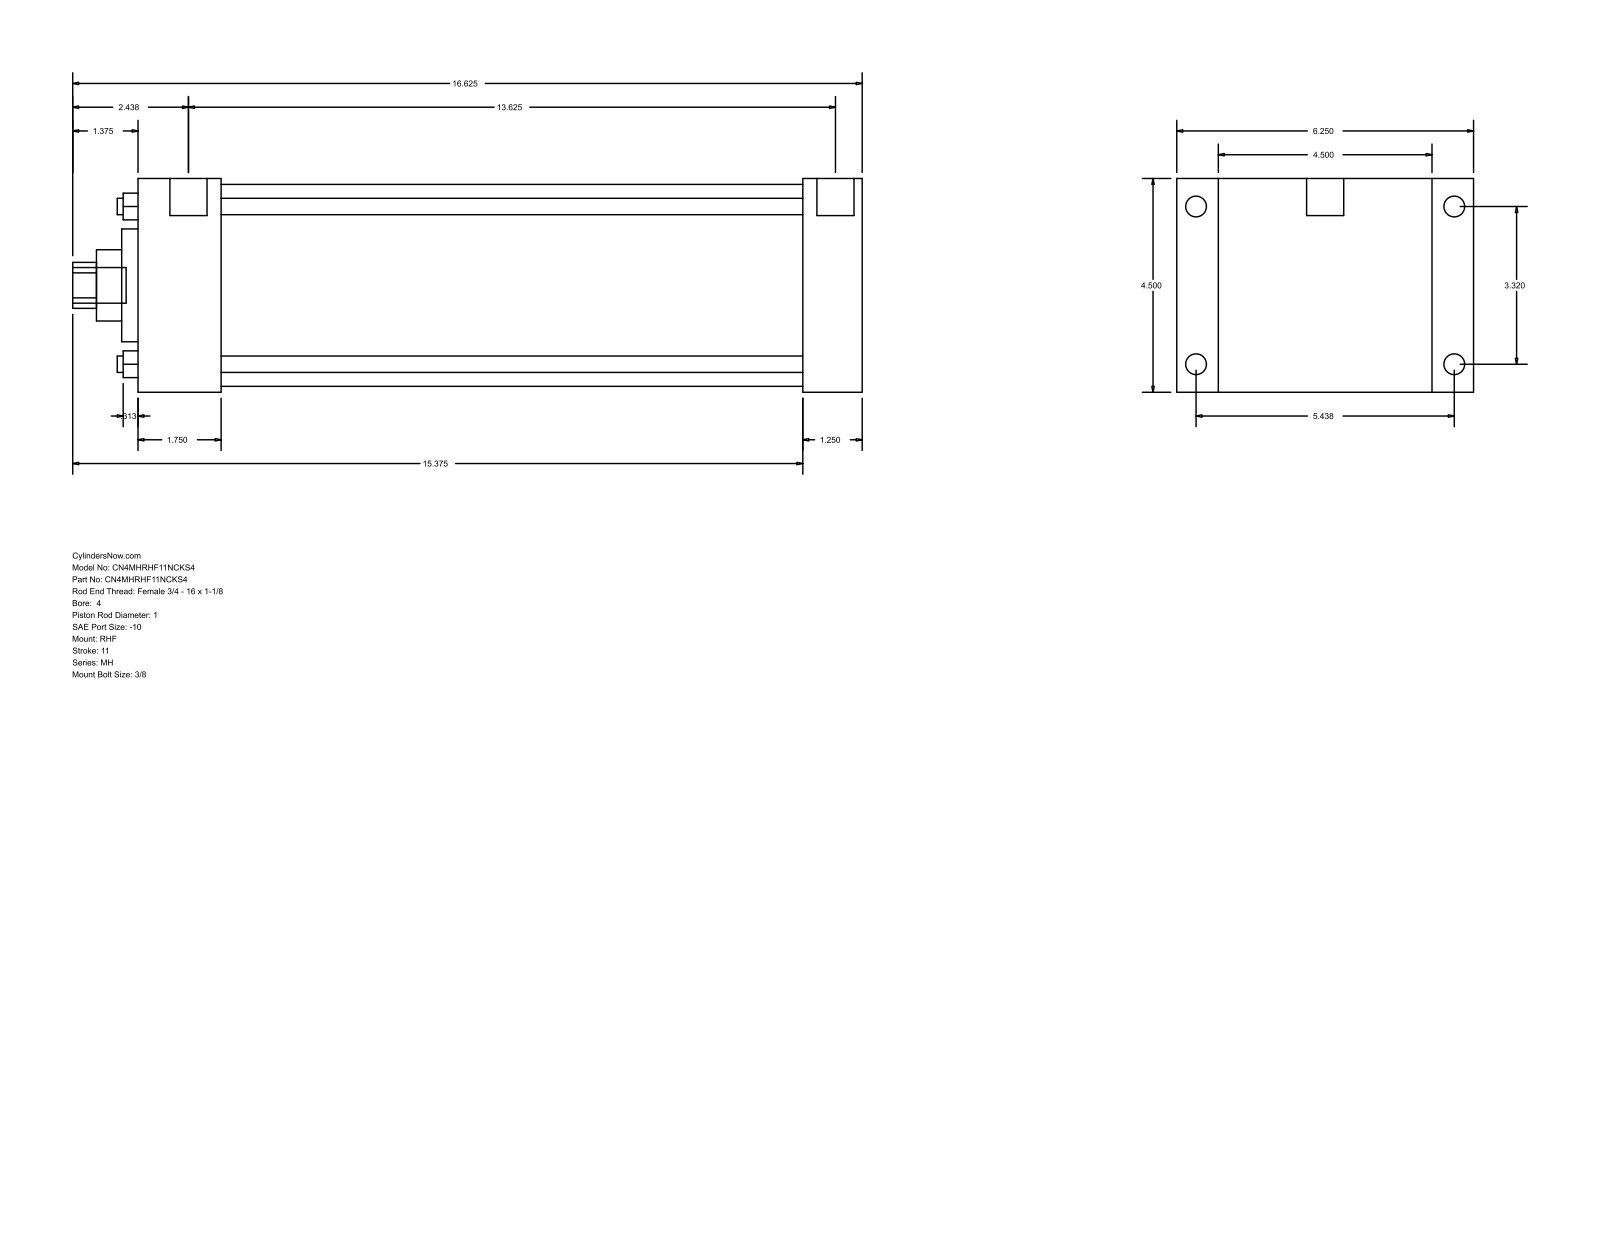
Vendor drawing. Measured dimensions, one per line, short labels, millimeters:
name: MH_RHF__0400_1
written by: GSSL Pune (CONFIG_CONTROL_DESIGN)
unit: mm
bodies: 0 solids, 90 faces (61 planar, 29 cylindrical, 0 other)
size: 422.27 × 158.75 × 114.3
holes: 4× ⌀8.76, 1× ⌀25.4, 1× ⌀38.1, 1× ⌀60.33, 1× ⌀107.95
bosses: 4× ⌀11.13, 4× ⌀8.73, 2× ⌀19.84, 1× ⌀19.05
rounds: 1× R12.29
face distances: 114.3, 387.35, 355.6, 31.75, 22.23, 136.53, 44.46, 311.14, 342.89, 158.76
hole spacings: 59.62, 84.32, 119.25
